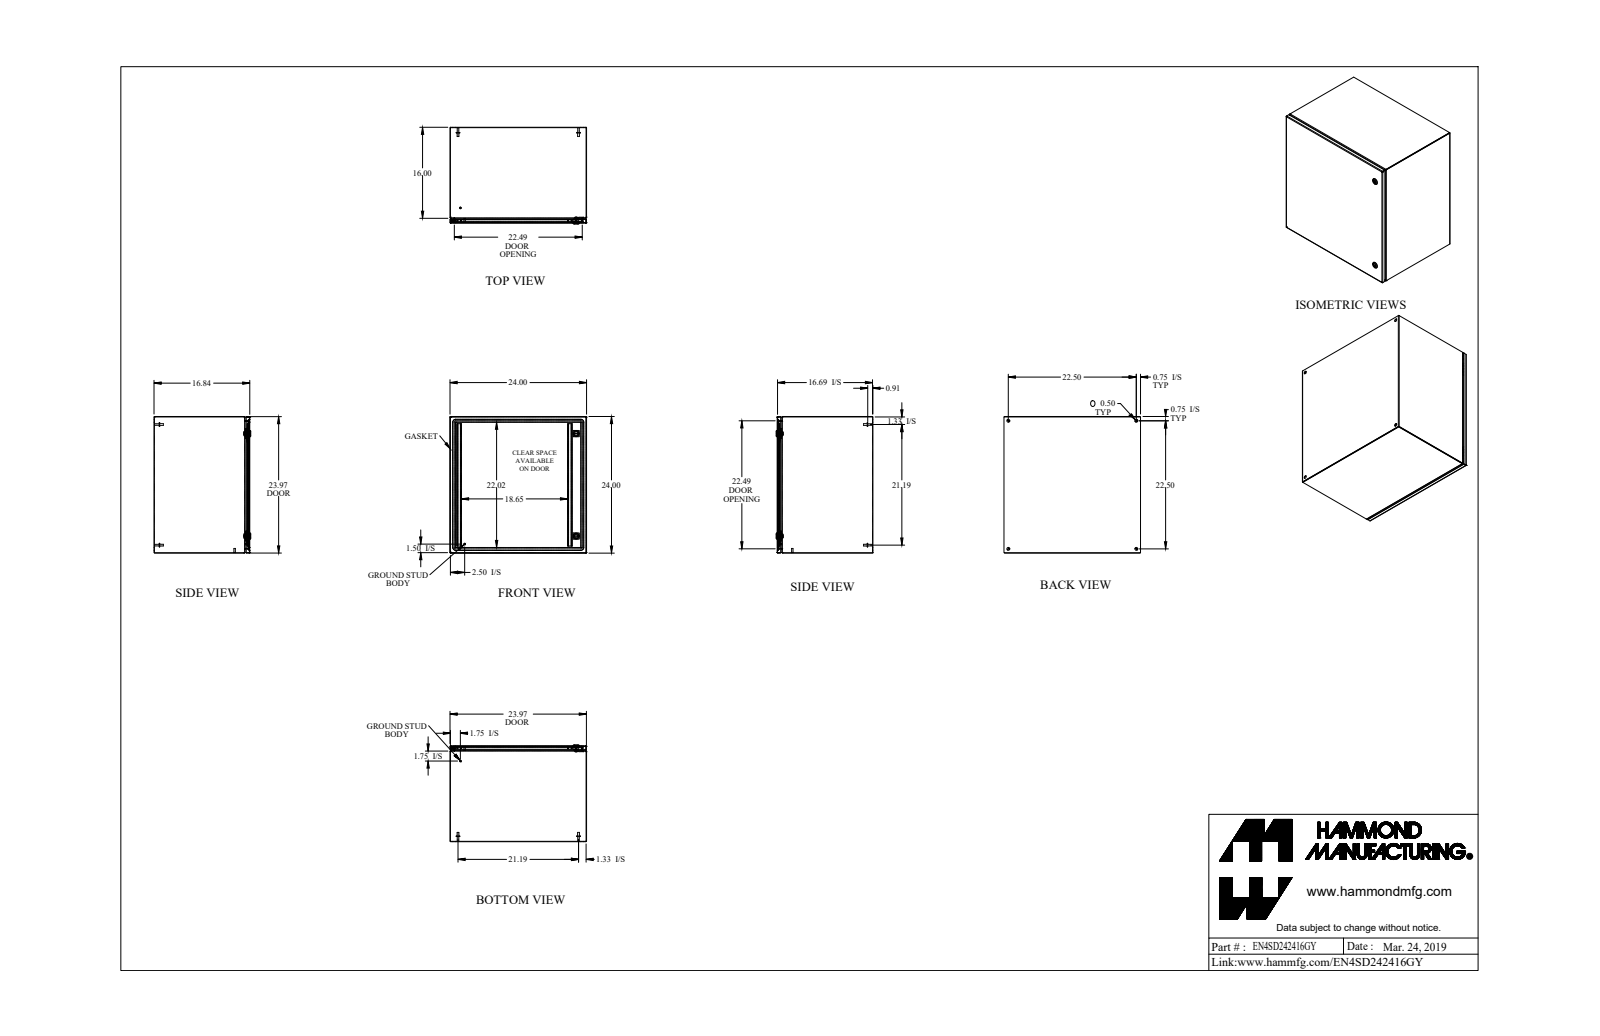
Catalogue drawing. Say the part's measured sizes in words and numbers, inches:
The part is named "EN4SD242416GY". Its 3-D file was written by "SolidWorks 2019 (AUTOMOTIVE_DESIGN)". It is 29 solids with 736 faces: 363 planar, 245 cylindrical and 128 other. Overall it measures 24 by 24 by 16.997 inches. Its volume is 218.8 cubic inches and its surface area 6 126 square inches. Round holes: 4 of diameter 0.5, 2 of diameter 0.232, 2 of diameter 0.625, 2 of diameter 0.785, 1 of diameter 0.172, 1 of diameter 0.24, 1 of diameter 0.242. Round bosses or shafts: 4 of diameter 0.625, 4 of diameter 0.313, 4 of diameter 0.27, 2 of diameter 1.1, 2 of diameter 0.525, 2 of diameter 0.281, 2 of diameter 0.25, 1 of diameter 0.455. Partial cylindrical surfaces (rounded edges, fillets, slot ends): 14 of radius 0.036, 14 of radius 0.108, 12 of radius 0.043, 12 of radius 0.081, 12 of radius 0.312, 8 of radius 0.1, 4 of radius 0.006, 4 of radius 0.062. The main face-to-face distances are 0.072, 23.928, 16.765, 23.856, 24, 16.693, 16.837, 0.837, 15.928, 0.75. The hole center spacings are 22.5, 31.82, 2.493, 2.494, 17.999, 20.277, 20.278, 21.544.
